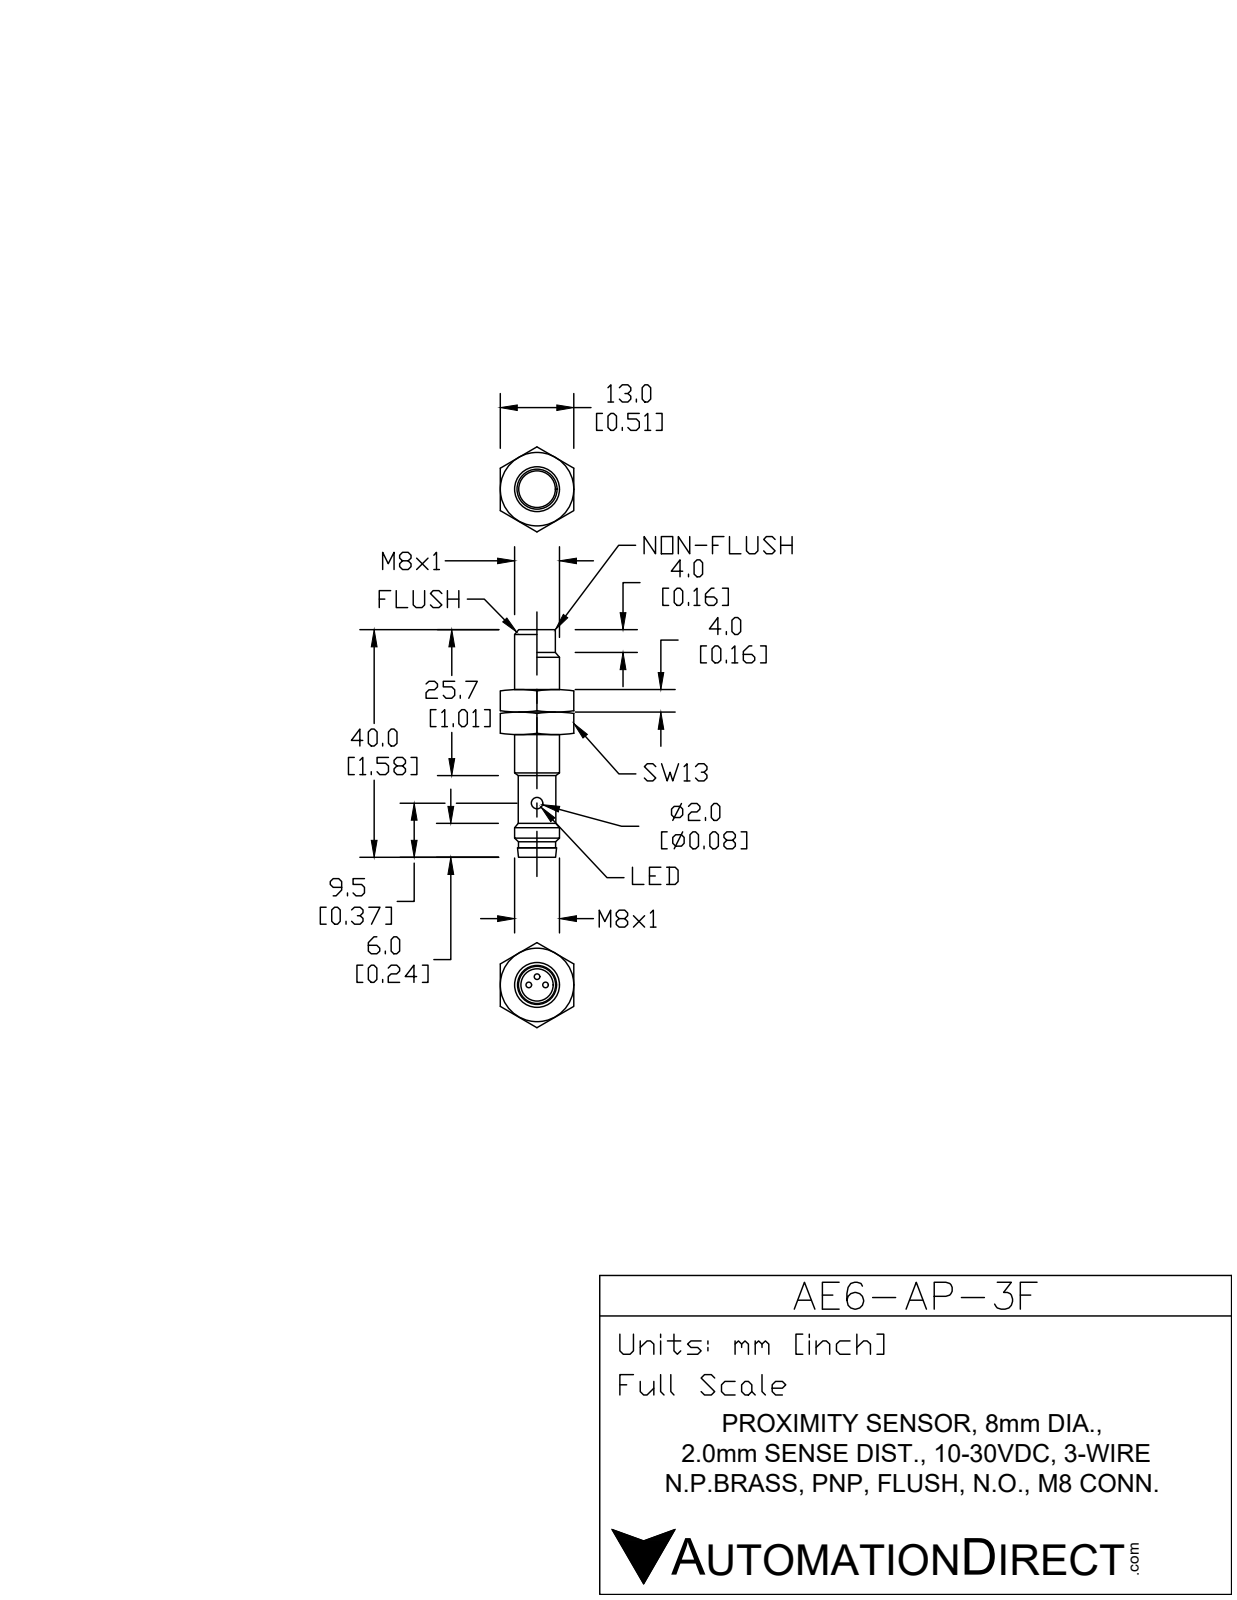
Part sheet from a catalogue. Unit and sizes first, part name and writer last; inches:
Units: inches
Overall size (bounding box): 1.575 × 0.315 × 0.315
Round holes (diameter × count): ⌀0.079 ×4, ⌀0.228 ×1
Round bosses / shafts (diameter × count): ⌀0.039 ×3, ⌀0.315 ×1, ⌀0.272 ×1, ⌀0.256 ×1, ⌀0.23 ×1
Main face-to-face distances: 1.122, 1.11, 1.299, 1.287, 0.177, 1.378, 1.366, 0.256, 0.079, 1.575
Volume: 0.109 in³ · Surface area: 2.26 in²
Bodies: 3 solids, 61 faces (11 planar, 30 cylindrical, 20 other)
Part name (STEP PRODUCT): AE6-AP-3F
STEP written by: SolidWorks 2017 (AUTOMOTIVE_DESIGN)
